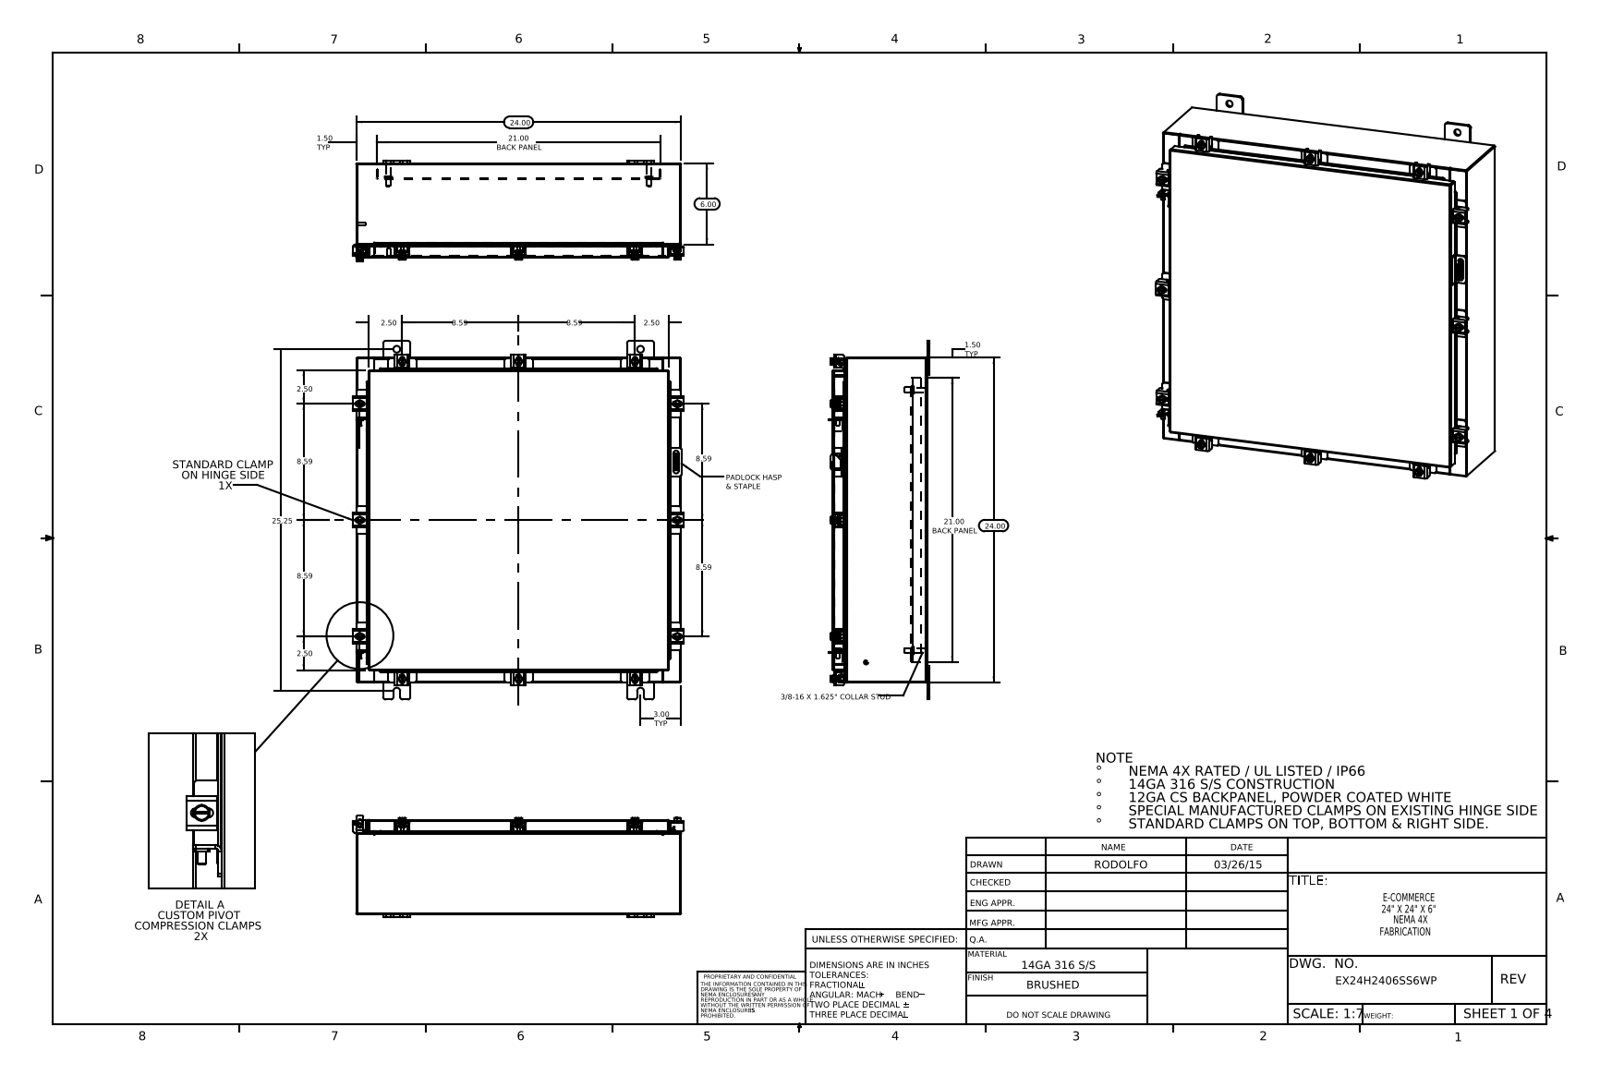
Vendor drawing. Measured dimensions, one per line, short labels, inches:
name: EX24H2406SS6WP Clamp Bracket; EX24H2406SS6WP Standard Clamps; EX24H2406SS6WP Padlock Hasp; EX24H2406SS6WP Cover (+8 more)
written by: SolidWorks 2014 (CONFIG_CONTROL_DESIGN)
unit: in
bodies: 81 solids, 2018 faces (1075 planar, 783 cylindrical, 160 other)
size: 26.5 × 24.421 × 7.453
volume: 202.2 in³; area: 5 023 in²
holes: 12× ⌀0.213, 12× ⌀0.26, 8× ⌀0.5, 1× ⌀0.125, 1× ⌀0.25
bosses: 12× ⌀0.5, 12× ⌀0.25, 10× ⌀0.399, 4× ⌀0.625, 4× ⌀0.375, 4× ⌀0.33, 2× ⌀0.315, 2× ⌀0.236
rounds: 54× R0.06, 24× R0.013, 24× R0.141, 24× R0.19, 22× R0.088, 22× R0.12, 18× R0.09, 17× R0.05
face distances: 0.075, 6.9, 23.925, 6.975, 6.826, 0.104, 1, 1.075, 5.826, 5.9
hole spacings: 8.594, 12.137, 20.559, 23.46, 24.976, 2.34, 18.34, 21.376
